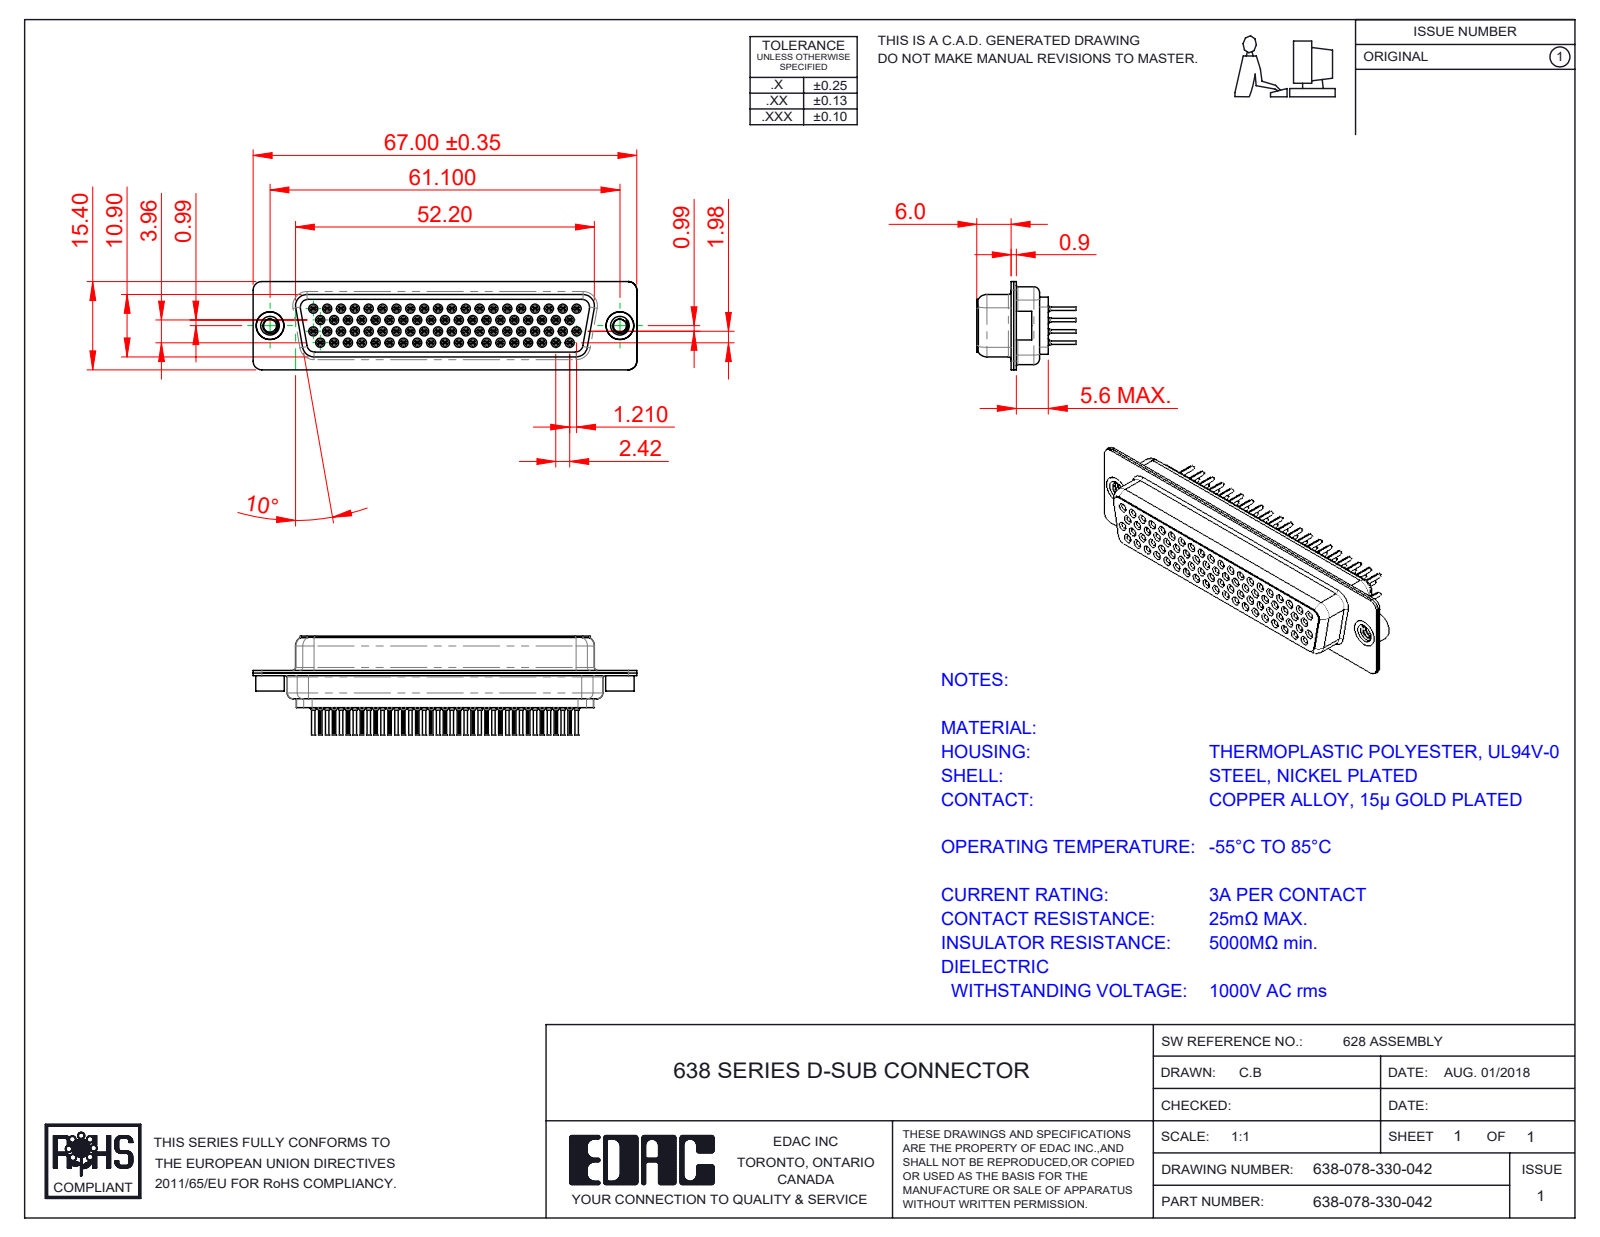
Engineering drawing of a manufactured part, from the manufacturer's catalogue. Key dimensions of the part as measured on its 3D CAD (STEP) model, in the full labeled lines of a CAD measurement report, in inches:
Part name (STEP PRODUCT): 638 Shell Front_78 Contacts; 638 Shell Rear_78 Contacts; 638 4-40 Threaded Rivet; 638 Contact Row 2_30 (+5 more)
STEP written by: SolidWorks 2020 (CONFIG_CONTROL_DESIGN)
Units: inches
Bodies: 83 solids, 10185 faces (2485 planar, 2711 cylindrical, 4989 other)
Overall size (bounding box): 2.638 × 0.681 × 0.606
Volume: 0.359 in³ · Surface area: 31.81 in²
Round holes (diameter × count): ⌀0.008 ×78, ⌀0.031 ×78, ⌀0.039 ×78, ⌀0.043 ×78, ⌀0.063 ×78, ⌀0.067 ×78, ⌀0.071 ×78, ⌀0.089 ×2, ⌀0.157 ×2, ⌀0.159 ×2, ⌀0.191 ×2
Round bosses / shafts (diameter × count): ⌀0.079 ×78, ⌀0.059 ×78, ⌀0.047 ×78, ⌀0.024 ×78, ⌀0.197 ×2, ⌀0.195 ×2, ⌀0.189 ×2, ⌀0.157 ×1
Partial cylindrical surfaces — rounded edges, fillets, slot ends (radius × count): R0.004 ×156, R0.011 ×39, R0.059 ×16, R0.079 ×12, R0.061 ×8, R0.01 ×4, R0.02 ×4, R0.022 ×4
Main face-to-face distances: 0.018, 0.016, 0.035, 0.053, 0.378, 0.465, 0.071, 0.449, 0.087, 0.518
Hole centre spacings: 0.095, 0.191, 0.286, 0.381, 0.239, 0.476, 0.274, 0.334
